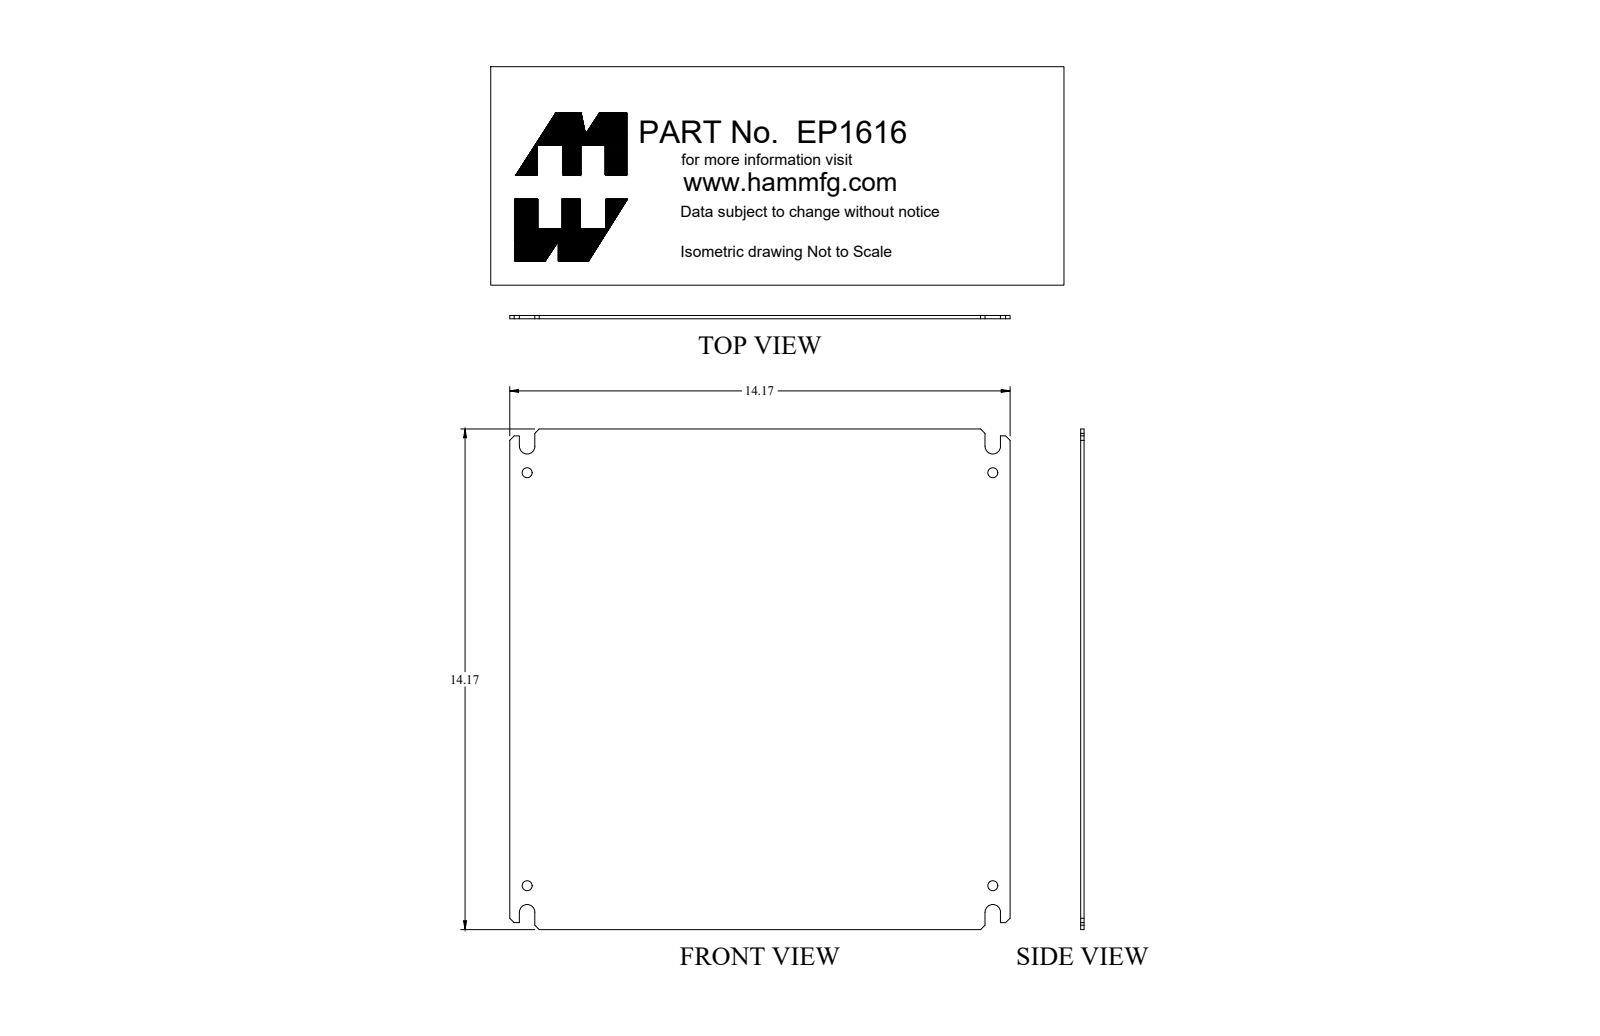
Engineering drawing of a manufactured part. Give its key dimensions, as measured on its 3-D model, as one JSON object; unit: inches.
{"part_name": "EP1616", "step_written_by": "SolidWorks 2018 (AUTOMOTIVE_DESIGN)", "units": "inches", "bodies": {"solids": 1, "faces": 40, "planar": 26, "cylindrical": 14, "other": 0}, "overall_size": [14.17, 14.17, 0.095], "volume_in3": 18.92, "surface_area_in2": 404.2, "round_holes": [[0.281, 4]], "partial_cylinders_radius": [[0.219, 4]], "face_to_face_distances": [0.095, 14.17, 0.709, 13.461, 0.272, 13.898, 0.437, 13.188, 12.751, 0.362], "hole_center_spacings": [11.688, 13.188, 17.622]}
